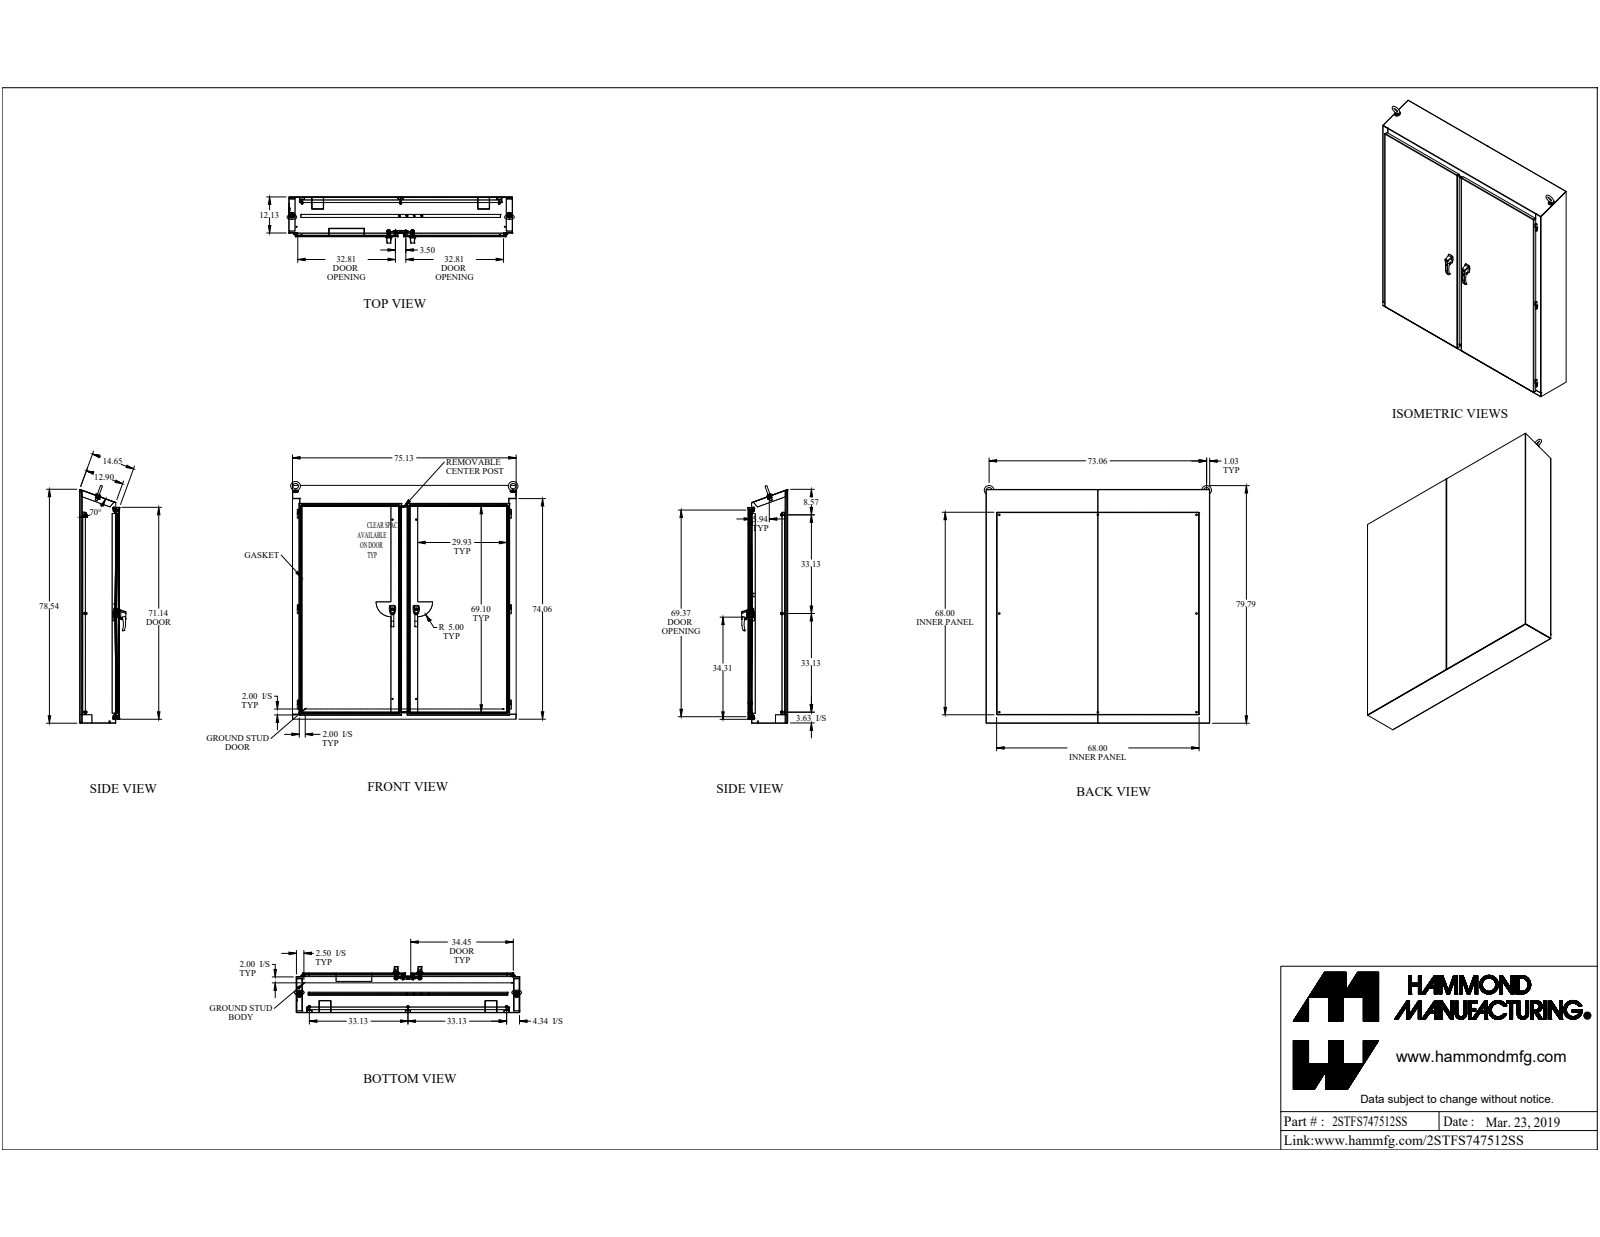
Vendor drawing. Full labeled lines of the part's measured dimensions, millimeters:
Part name (STEP PRODUCT): 2STFS747512SS
STEP written by: SolidWorks 2019 (CONFIG_CONTROL_DESIGN)
Units: millimetres
Bodies: 146 solids, 2404 faces (1417 planar, 729 cylindrical, 258 other)
Overall size (bounding box): 2026.7 × 1938.2 × 393.5
Volume: 39 560 000 mm³ · Surface area: 30 860 000 mm²
Round holes (diameter × count): ⌀7.8 ×8, ⌀8.9 ×8, ⌀14.3 ×8, ⌀6.4 ×7, ⌀7.1 ×6, ⌀8 ×6, ⌀11.3 ×6, ⌀5 ×4, ⌀6.5 ×4, ⌀7.1 ×4, ⌀9.9 ×4, ⌀10.5 ×4
Round bosses / shafts (diameter × count): ⌀25.4 ×12, ⌀16.5 ×8, ⌀9.5 ×8, ⌀8.4 ×8, ⌀19.1 ×4, ⌀16 ×4, ⌀15.9 ×4, ⌀11.2 ×4
Partial cylindrical surfaces — rounded edges, fillets, slot ends (radius × count): R3.2 ×47, R12.7 ×33, R0.5 ×32, R1.2 ×30, R3.6 ×30, R1.5 ×20, R6.4 ×16, R0.8 ×12
Main face-to-face distances: 2.4, 2.4, 334.9, 337.3, 337.3, 339.8, 3.2, 291.3, 288.9, 46
Hole centre spacings: 1855.7, 202.8, 1881.4, 1682.8, 189.1, 750.4, 764.5, 764.6
